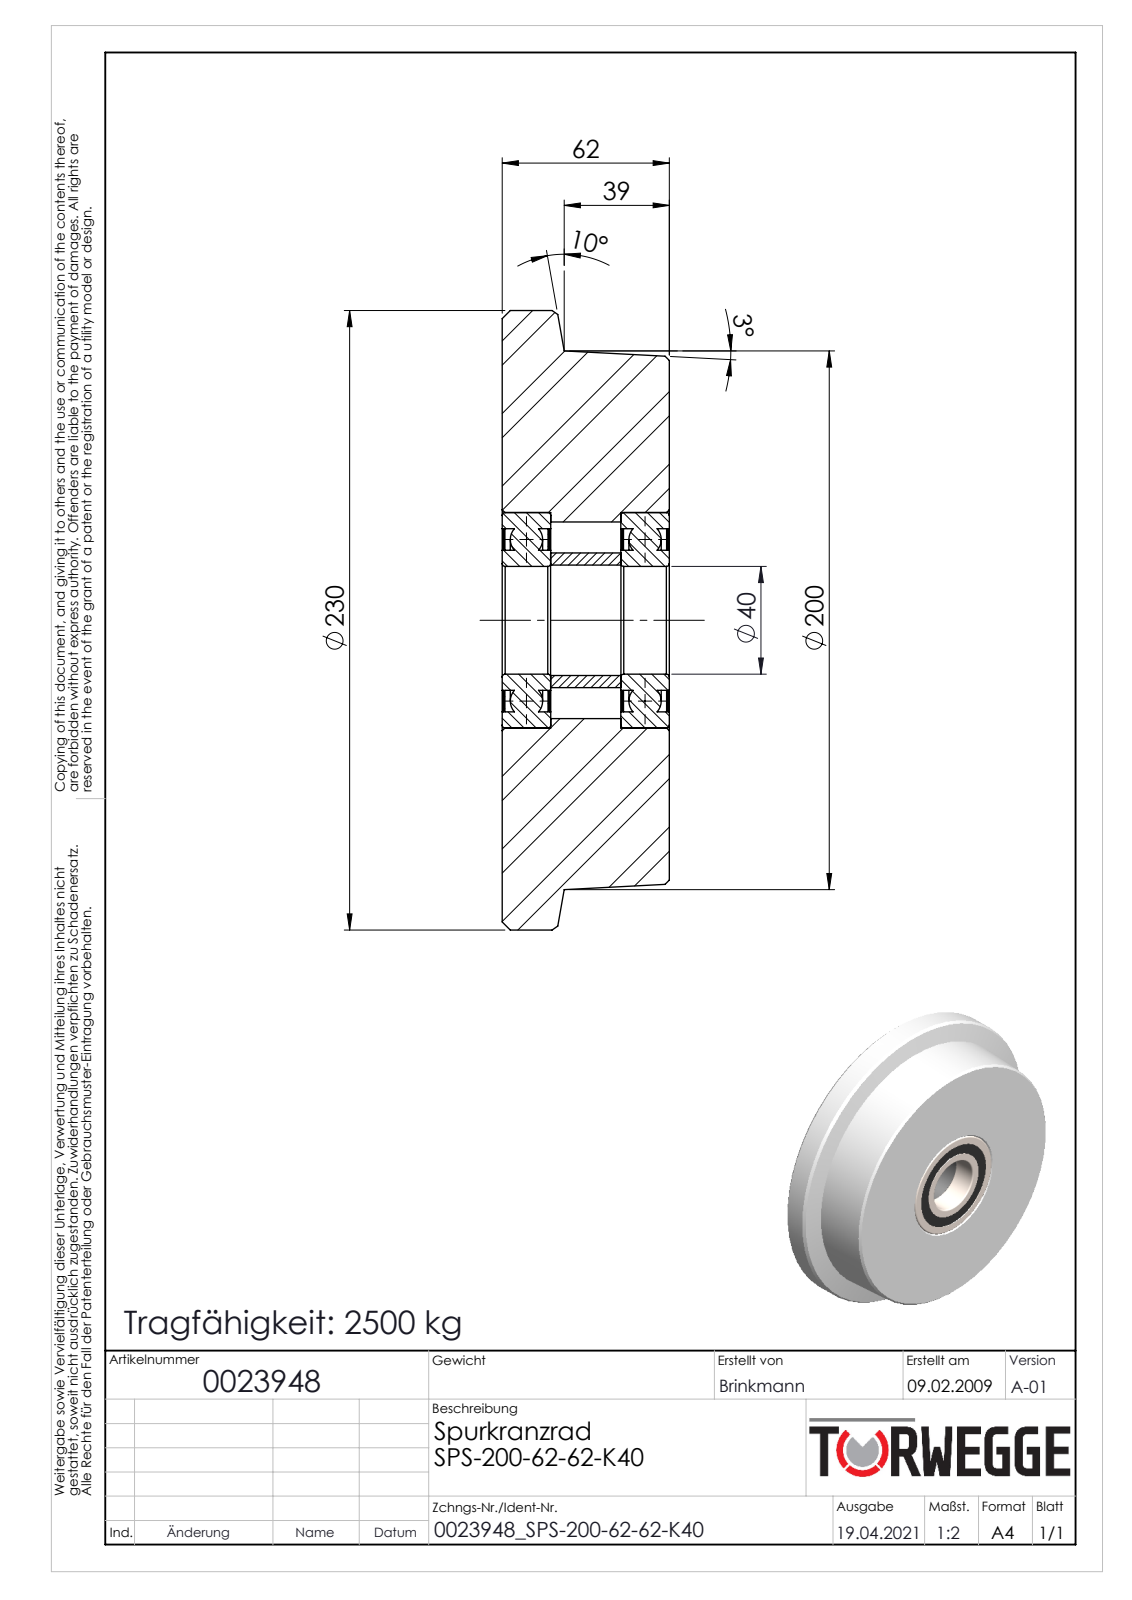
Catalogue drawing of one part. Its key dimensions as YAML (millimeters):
part_name: "0023948"
step_written_by: "SolidWorks 2020 (AUTOMOTIVE_DESIGN)"
units: millimeters
bodies: {solids: 4, faces: 112, planar: 22, cylindrical: 52, other: 38}
overall_size: [230, 230, 62]
volume: 1981000
surface_area: 180349
round_holes:
  - {diameter: 40, count: 1}
  - {diameter: 41, count: 1}
  - {diameter: 68, count: 1}
  - {diameter: 73, count: 1}
  - {diameter: 80, count: 1}
round_bosses_or_shafts:
  - {diameter: 230, count: 1}
  - {diameter: 52, count: 1}
  - {diameter: 50, count: 1}
face_to_face_distances: [62, 0.5, 44, 17, 1, 17.5, 44.5, 16.5, 43.5, 18]
